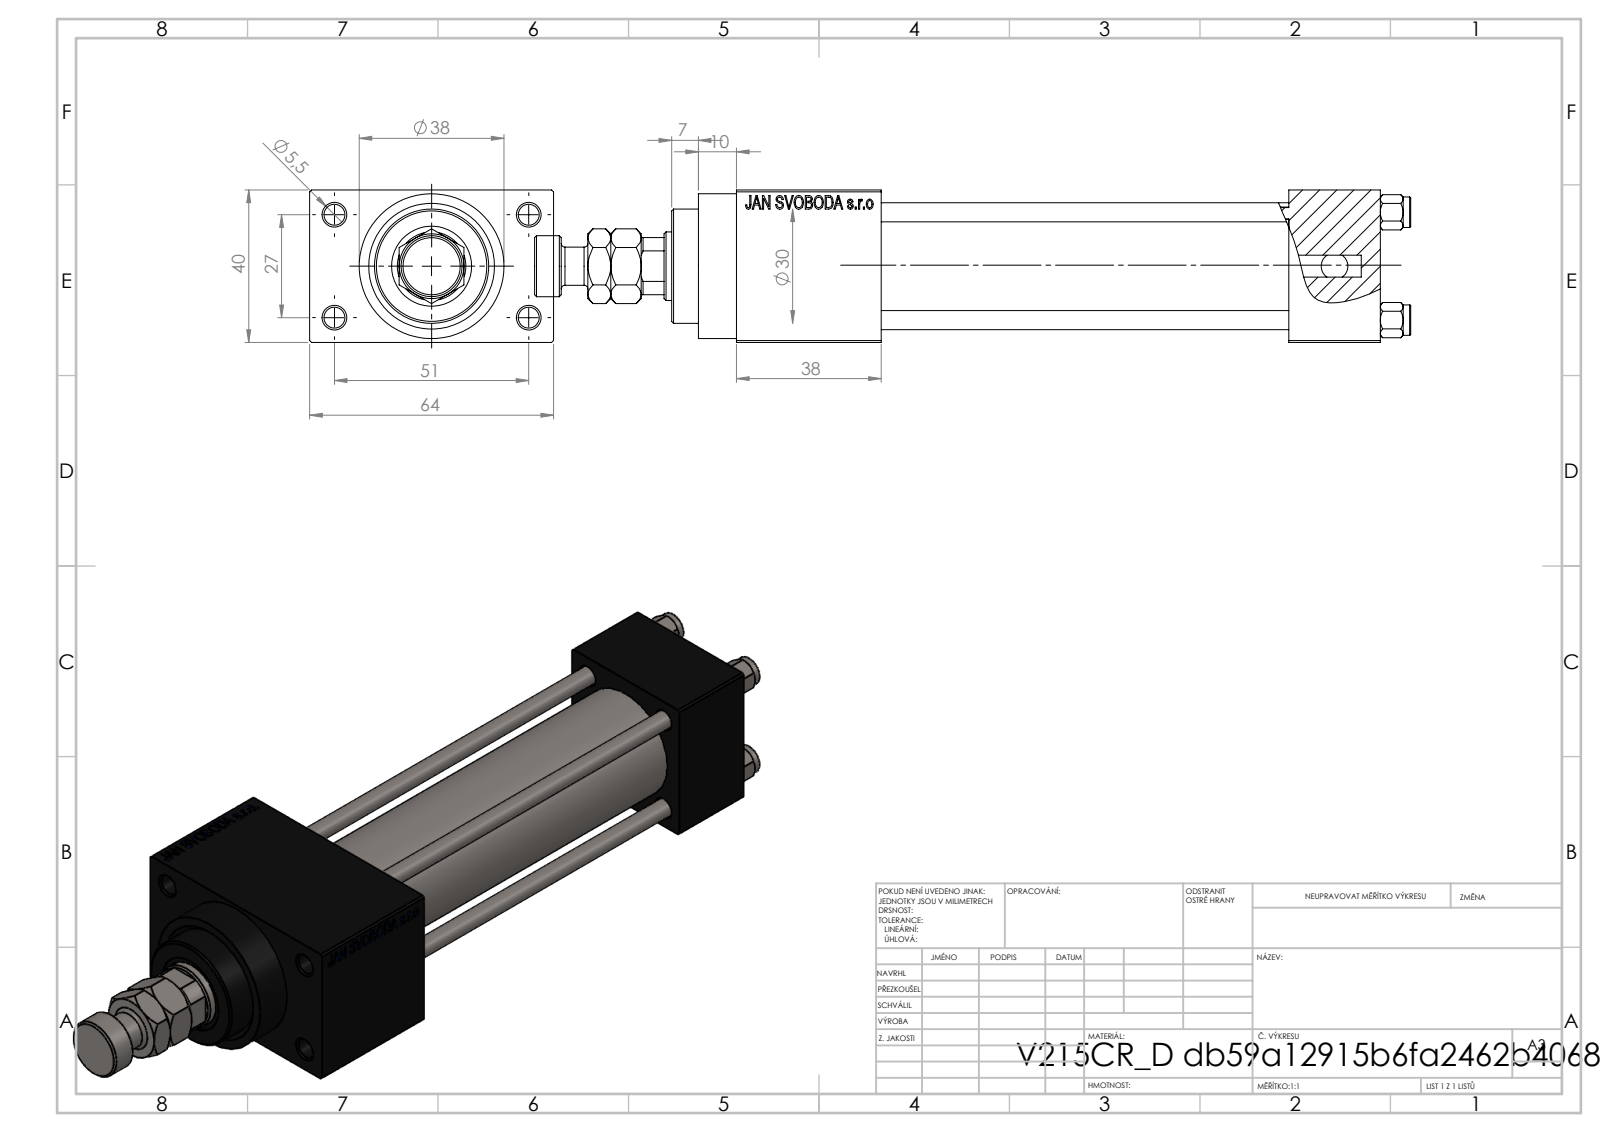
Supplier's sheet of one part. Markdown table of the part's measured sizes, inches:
| quantity | value |
| --- | --- |
| part name | V215CR_VCP_D; V215CR_D_Body; V215CR_D_TYCINKA; NUT_M5_D (+2 more) |
| STEP written by | SolidWorks 2019 (CONFIG_CONTROL_DESIGN) |
| units | inches |
| bodies | 12 solids, 1153 faces (511 planar, 90 cylindrical, 552 other) |
| overall size | 9.055 × 2.52 × 1.575 |
| volume | 13.45 in³ |
| surface area | 130.8 in² |
| round holes (diameter × count) | 0.197 × 4, 0.217 × 4, 0.787 × 3, 0.276 × 2, 0.518 × 2, 0.335 × 1, 0.709 × 1, 0.827 × 1, 0.984 × 1, 1.181 × 1 |
| round bosses / shafts (diameter × count) | 0.315 × 4, 1.496 × 1, 1.22 × 1, 0.63 × 1, 0.394 × 1 |
| partial cylindrical surfaces (radius × count) | 0.335 × 1 |
| main face-to-face distances | 1.575, 0.472, 4.213, 0.945, 5.157, 2.047, 1.496, 6.654, 5.709, 2.52 |
| hole center spacings | 0.448, 0.788, 1.114, 1.136, 1.177, 1.561, 1.903, 1.063 |
